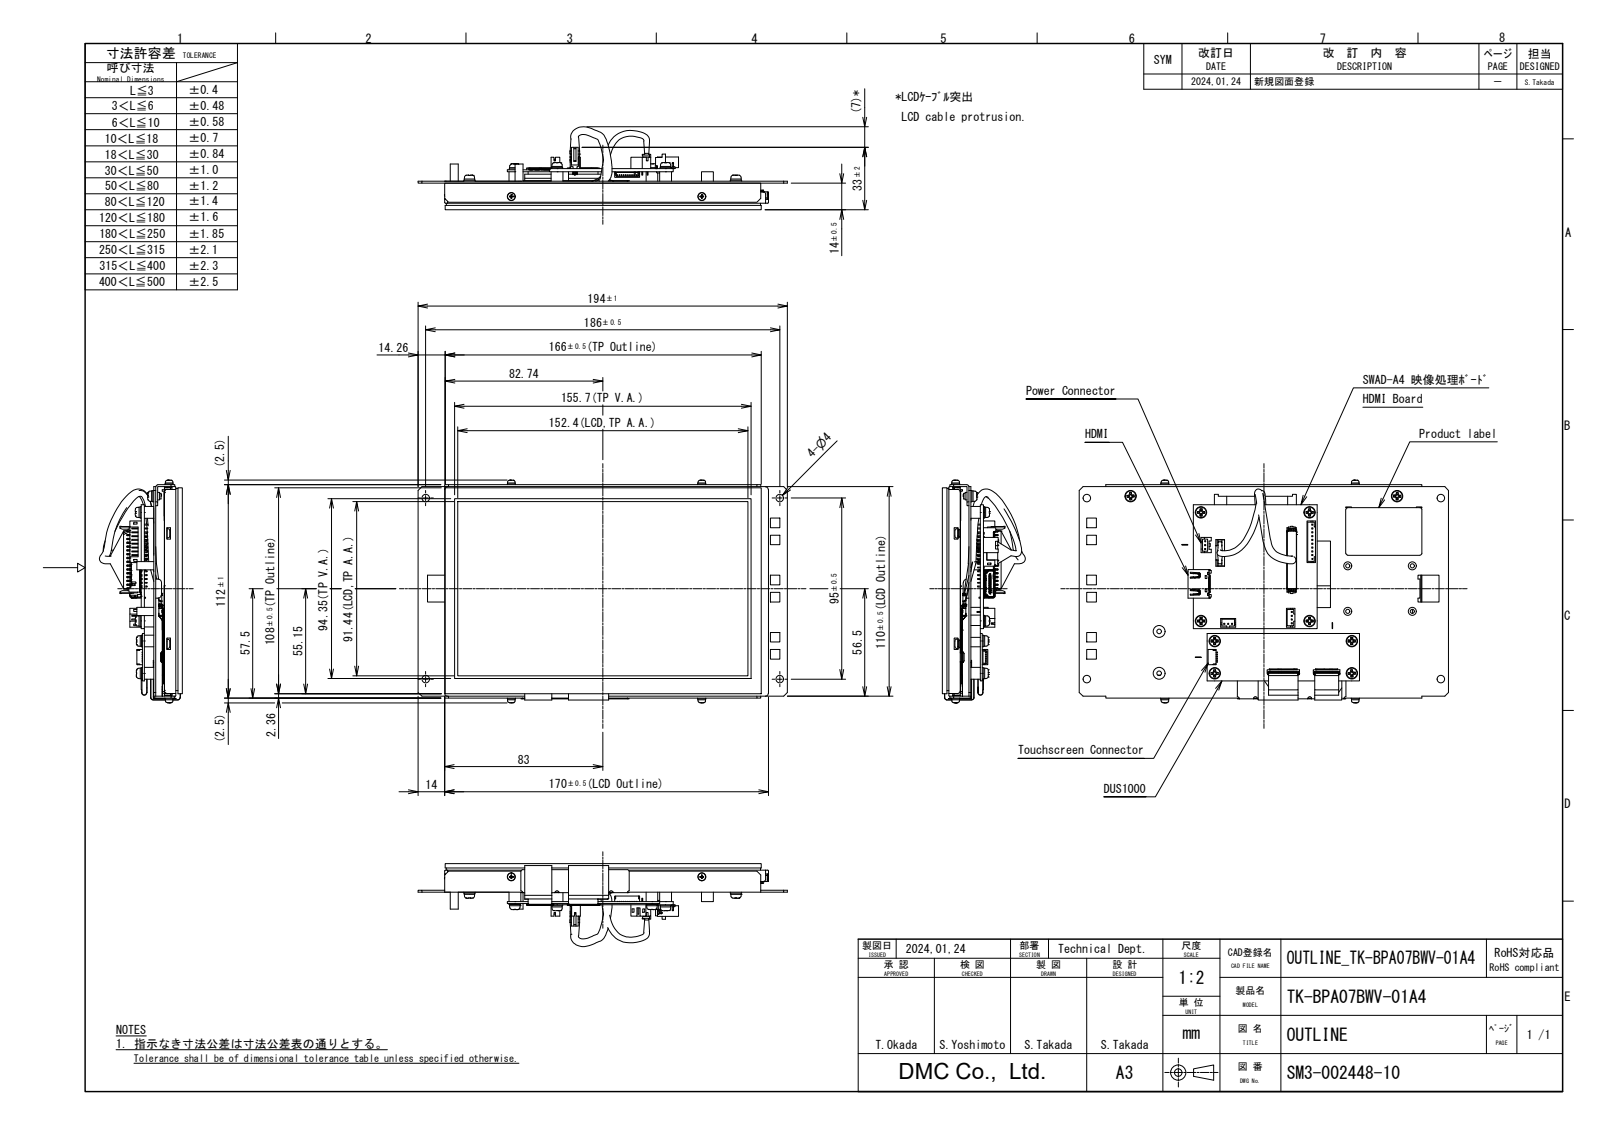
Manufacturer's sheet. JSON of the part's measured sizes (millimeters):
{"part_name": "HP_TK-BPA07BWV-01A4", "step_written_by": "Autodesk Inventor 2020 (AUTOMOTIVE_DESIGN)", "units": "millimeters", "bodies": {"solids": 1, "faces": 12398, "planar": 9460, "cylindrical": 2346, "other": 592}, "overall_size": [194, 116.97, 43.57], "volume_mm3": 119526, "surface_area_mm2": 236137, "round_holes": [[2.46, 10], [3.5, 8], [8, 8], [0.4, 4], [2.11, 4], [2.4, 4], [4, 4], [2, 2], [3, 2], [5, 2], [2.1, 1], [8.4, 1]], "round_bosses_or_shafts": [[6.2, 10], [6, 10], [5.5, 10], [3, 10], [3.6, 8], [4.2, 4], [4, 4], [2, 4]], "partial_cylinders_radius": [[0.5, 272], [0.2, 180], [0.3, 101], [1, 95], [0.1, 79], [0.25, 29], [0.15, 26], [1.1, 26]], "face_to_face_distances": [6.32, 1.75, 1, 0.8, 2.35, 9.47, 8.67, 7.12, 5.3, 4.5], "hole_center_spacings": [57, 127.08, 133.5, 43.32, 11.3, 11.35, 11.36, 17]}
